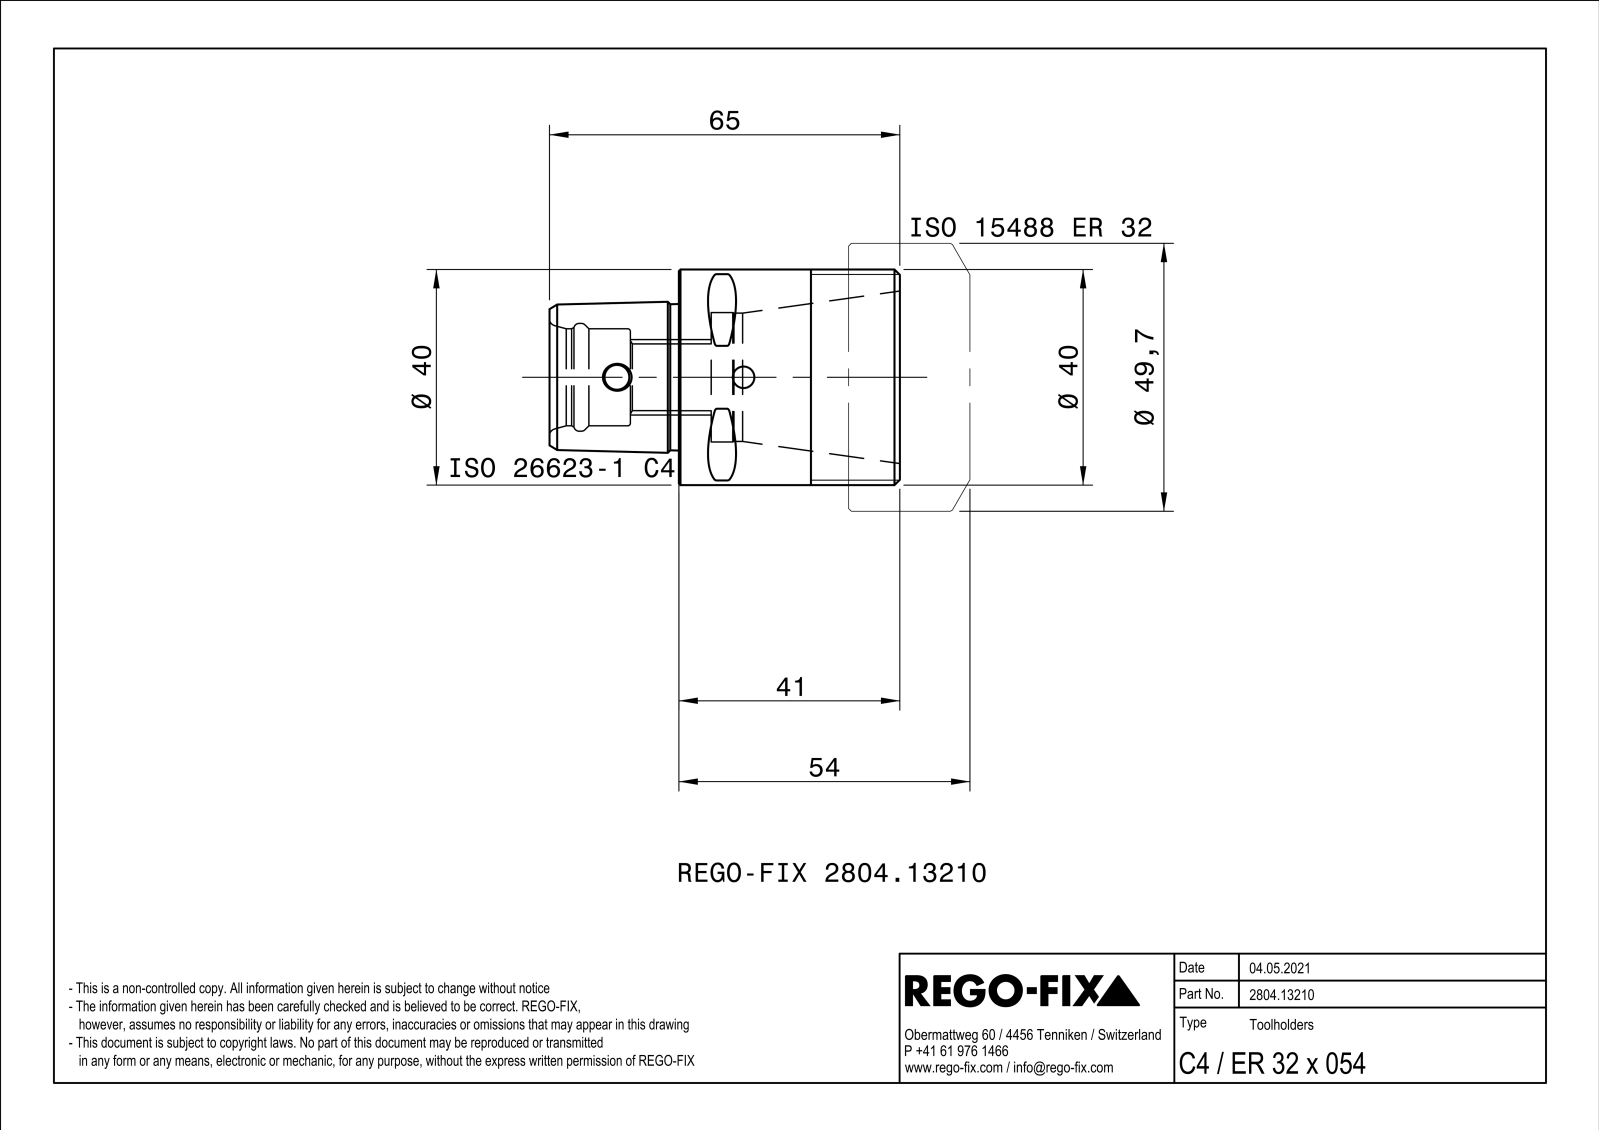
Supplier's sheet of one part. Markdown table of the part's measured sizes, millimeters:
| quantity | value |
| --- | --- |
| part name | NOCUT |
| STEP written by | SIEMENS PLM Software Solid Edge ST10 (AUTOMOTIVE_DESIGN) |
| units | millimeters |
| bodies | 1 solid, 100 faces (20 planar, 20 cylindrical, 60 other) |
| overall size | 65 × 40 × 40 |
| volume | 38 312 mm³ |
| surface area | 13 621 mm² |
| round holes (diameter × count) | 4 × 1, 4.6 × 1, 12.38 × 1, 18 × 1, 20 × 1, 23.8 × 1, 24 × 1 |
| round bosses / shafts (diameter × count) | 40 × 1 |
| partial cylindrical surfaces (radius × count) | 0.5 × 8, 3 × 1 |
| main face-to-face distances | 6, 35, 41, 15, 65, 30, 24, 15.52, 50, 9 |
| hole center spacings | 23.5 |
